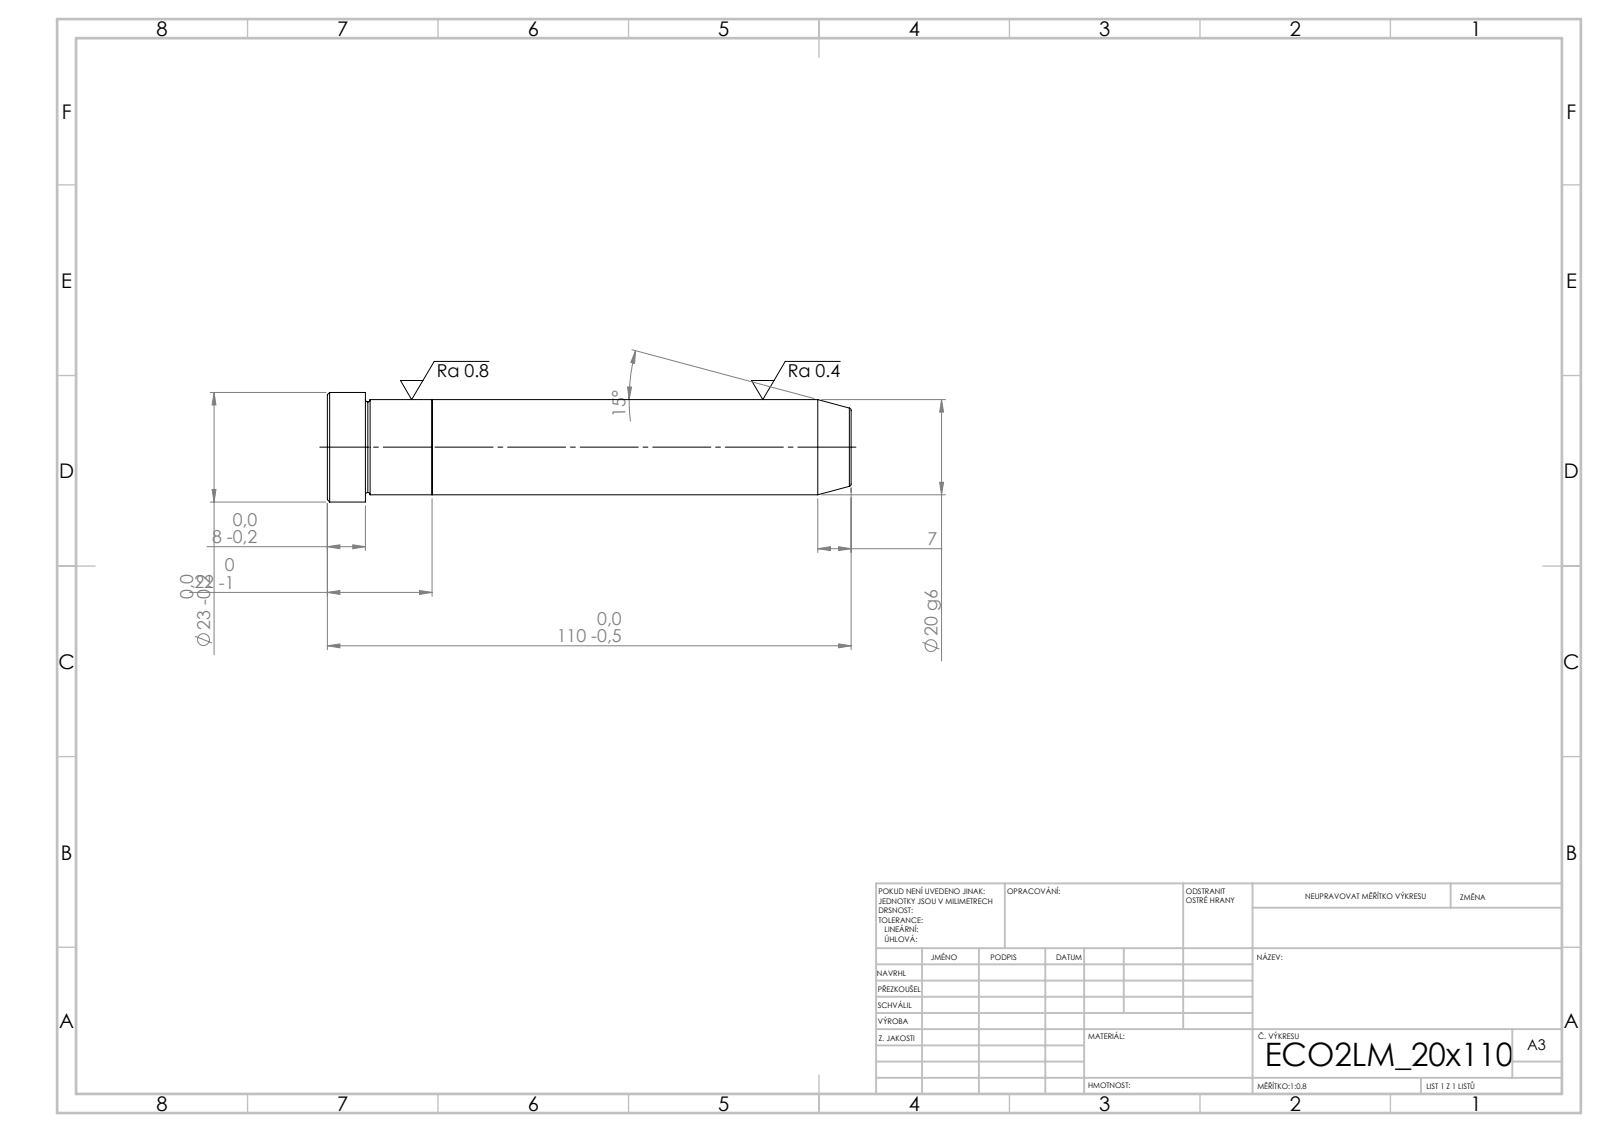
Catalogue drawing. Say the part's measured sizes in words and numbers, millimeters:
Its 3-D file was written by "SolidWorks 2019 (CONFIG_CONTROL_DESIGN)". It is 2 solids with 21 faces: 5 planar, 6 cylindrical and 10 other. Overall it measures 110 by 23 by 23 millimeters. Its volume is 34 947 cubic millimeters and its surface area 8 318 square millimeters. Round bosses or shafts: 1 of diameter 23, 1 of diameter 20. The main face-to-face distances are 22, 88, 110, 102, 14, 8.
